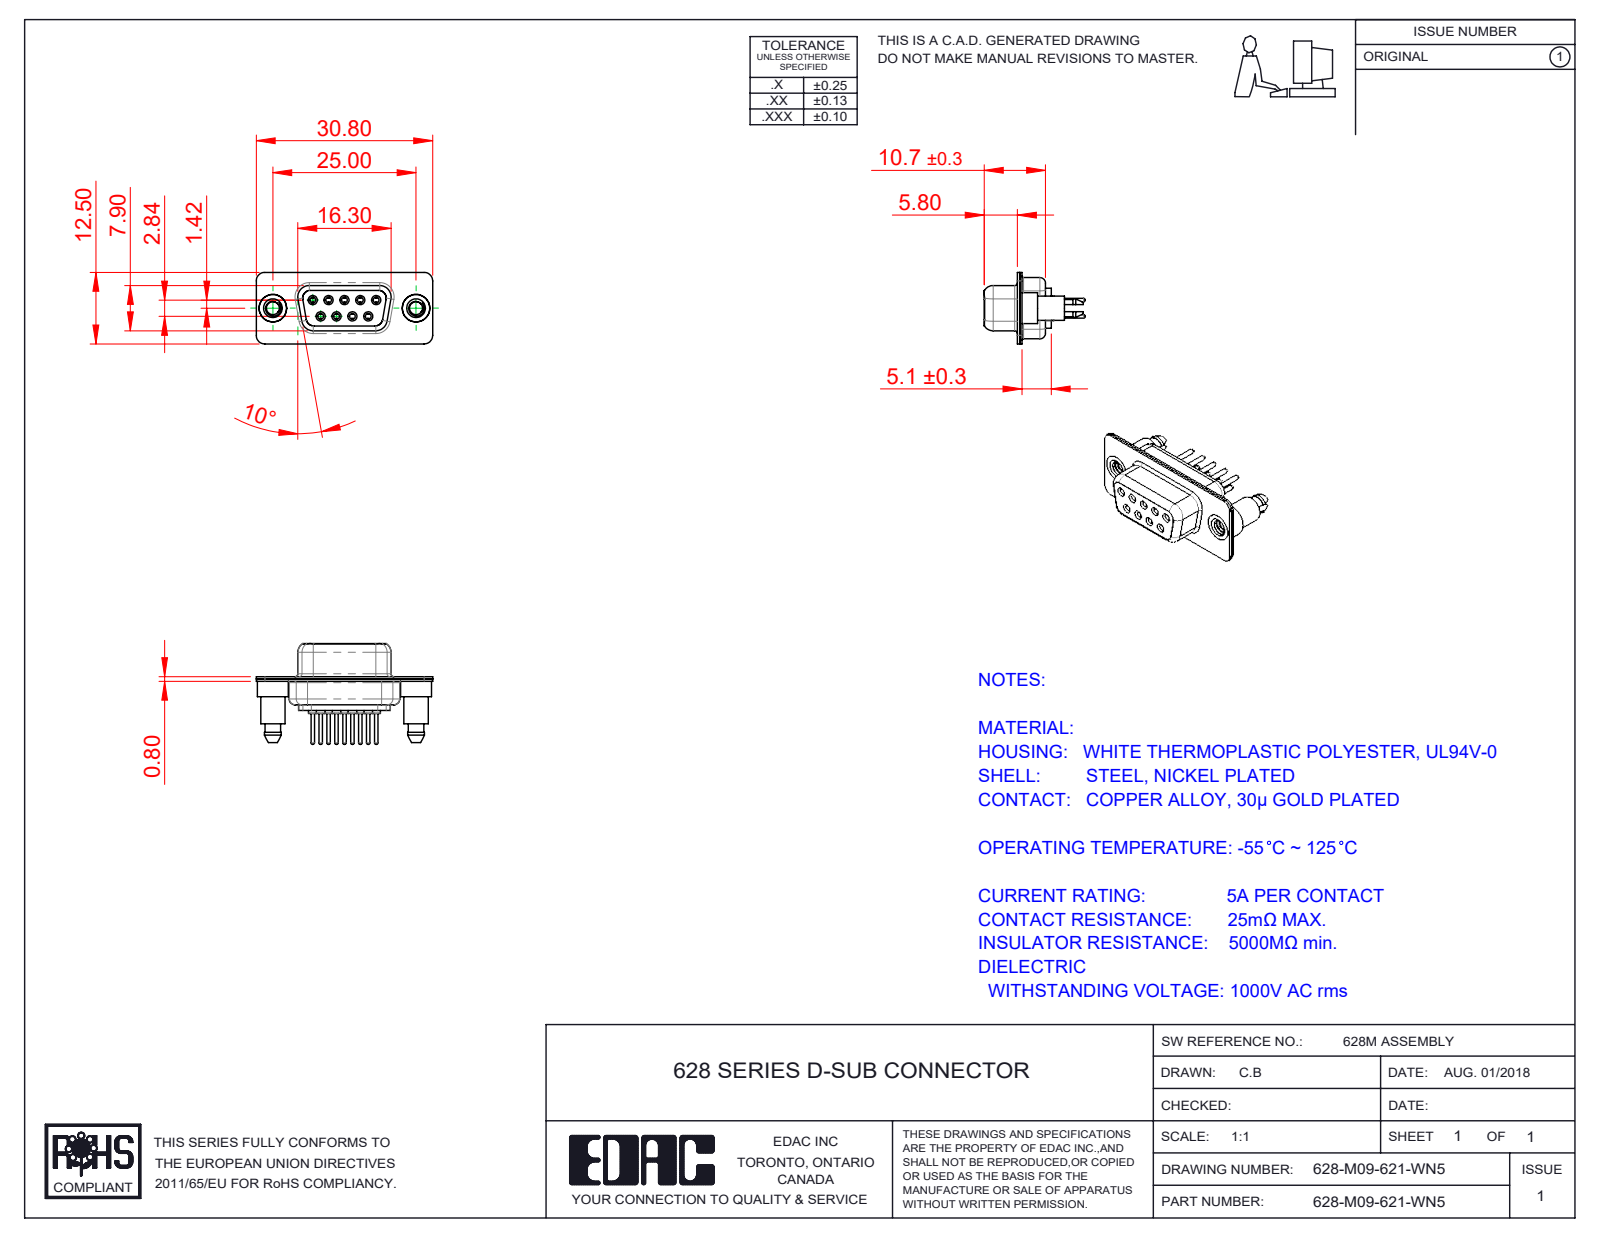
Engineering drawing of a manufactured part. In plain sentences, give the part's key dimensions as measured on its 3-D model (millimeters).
The part is named "628M Shell Rear_09 Contacts; 628-M09-621-WN5; 628M Housing_09 Contacts; 628M Contact Row 2_21 (+3 more)". Its 3-D file was written by "SolidWorks 2020 (CONFIG_CONTROL_DESIGN)". It is 14 solids with 824 faces: 218 planar, 340 cylindrical and 266 other. Overall it measures 30.8 by 17.6 by 12.5 millimeters. Its volume is 1 836 cubic millimeters and its surface area 4 755 square millimeters. Round holes: 9 of diameter 1, 9 of diameter 1.1, 9 of diameter 1.7, 9 of diameter 1.8, 9 of diameter 2, 2 of diameter 2.26, 2 of diameter 4, 2 of diameter 4.8. Round bosses or shafts: 9 of diameter 2.2, 9 of diameter 1.6, 9 of diameter 1.5, 9 of diameter 0.6, 2 of diameter 5.4, 2 of diameter 4.9, 2 of diameter 4.25. Partial cylindrical surfaces (rounded edges, fillets, slot ends): 18 of radius 1.5, 12 of radius 2, 10 of radius 1.6, 8 of radius 1.35, 4 of radius 0.25, 4 of radius 0.5, 4 of radius 0.6, 4 of radius 0.65. The main face-to-face distances are 0.4, 1.4, 0.45, 8.45, 0.8, 1.8, 1, 8.9, 6.2, 7.05. The hole center spacings are 3.16, 2.77, 5.54, 5.03, 5.04, 8.31, 7.1, 7.48.
